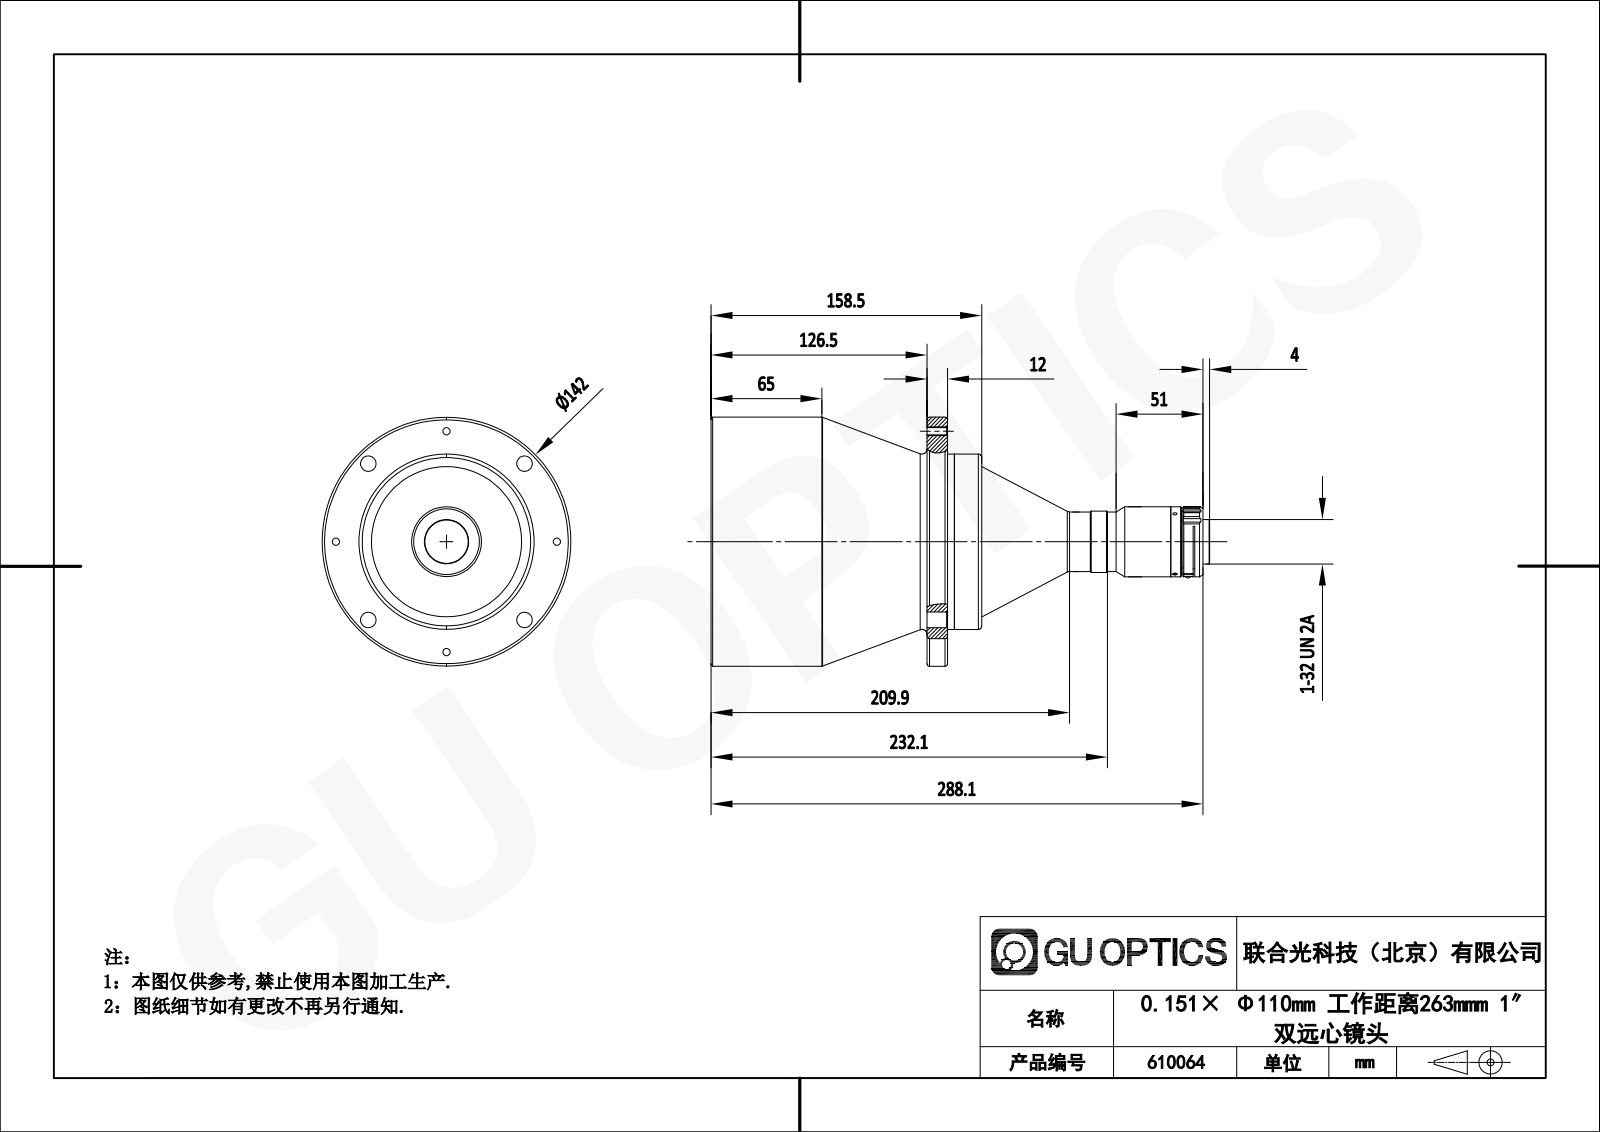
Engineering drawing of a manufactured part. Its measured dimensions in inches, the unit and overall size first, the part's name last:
Units: inches
Overall size (bounding box): 11.5 × 5.591 × 5.591
Round holes (diameter × count): ⌀0.165 ×4, ⌀0.354 ×4, ⌀0.098 ×3
Round bosses / shafts (diameter × count): ⌀5.591 ×1, ⌀3.937 ×1, ⌀1.575 ×1, ⌀1.378 ×1, ⌀1.339 ×1, ⌀1.299 ×1, ⌀1 ×1
Main face-to-face distances: 5.453, 4.98, 0.472, 6.24, 1.26, 0.787, 11.343, 6.362, 5.89, 5.102
Hole centre spacings: 1.898, 3.508, 4.583, 4.961, 4.961
Volume: 141.3 in³ · Surface area: 188.4 in²
Bodies: 1 solid, 86 faces (8 planar, 42 cylindrical, 36 other)
Part name (STEP PRODUCT): DTCM110-110-AL
STEP written by: SolidWorks 2017 (CONFIG_CONTROL_DESIGN)
